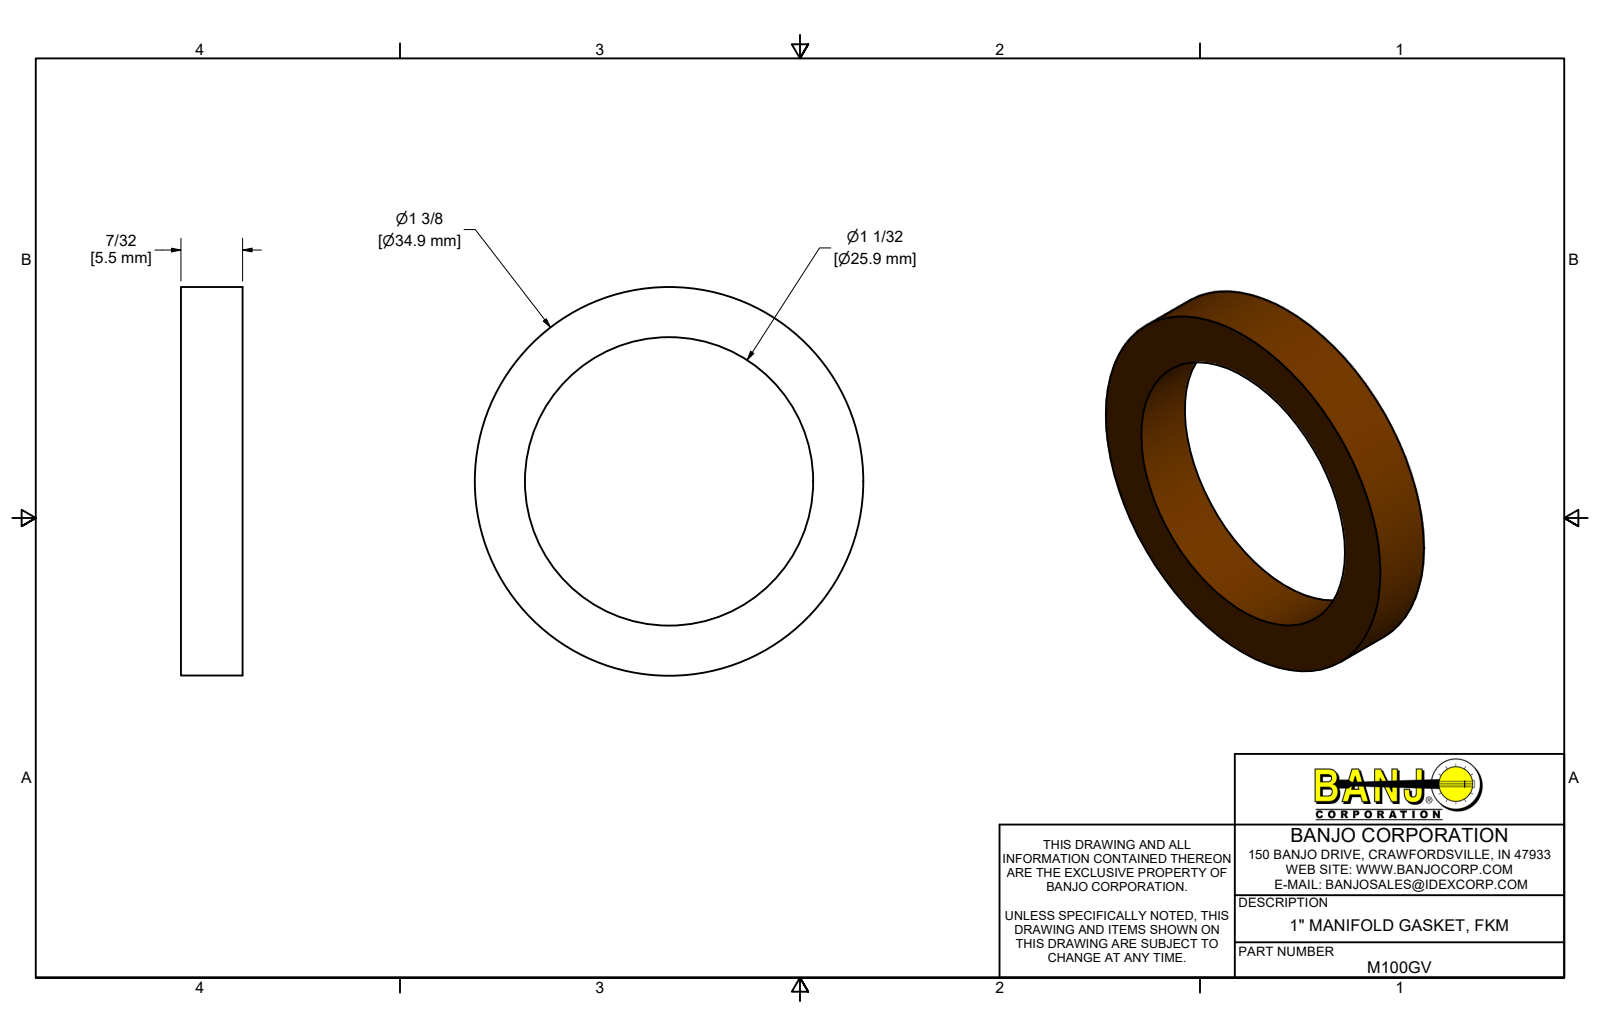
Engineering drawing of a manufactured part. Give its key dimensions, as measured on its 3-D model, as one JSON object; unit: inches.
{"part_name": "M100GV", "step_written_by": "Autodesk Inventor 2019 (AUTOMOTIVE_DESIGN)", "units": "inches", "bodies": {"solids": 1, "faces": 4, "planar": 2, "cylindrical": 2, "other": 0}, "overall_size": [1.375, 1.375, 0.218], "volume_in3": 0.146, "surface_area_in2": 2.976, "round_holes": [[1.02, 1]], "round_bosses_or_shafts": [[1.375, 1]], "face_to_face_distances": [0.218]}
